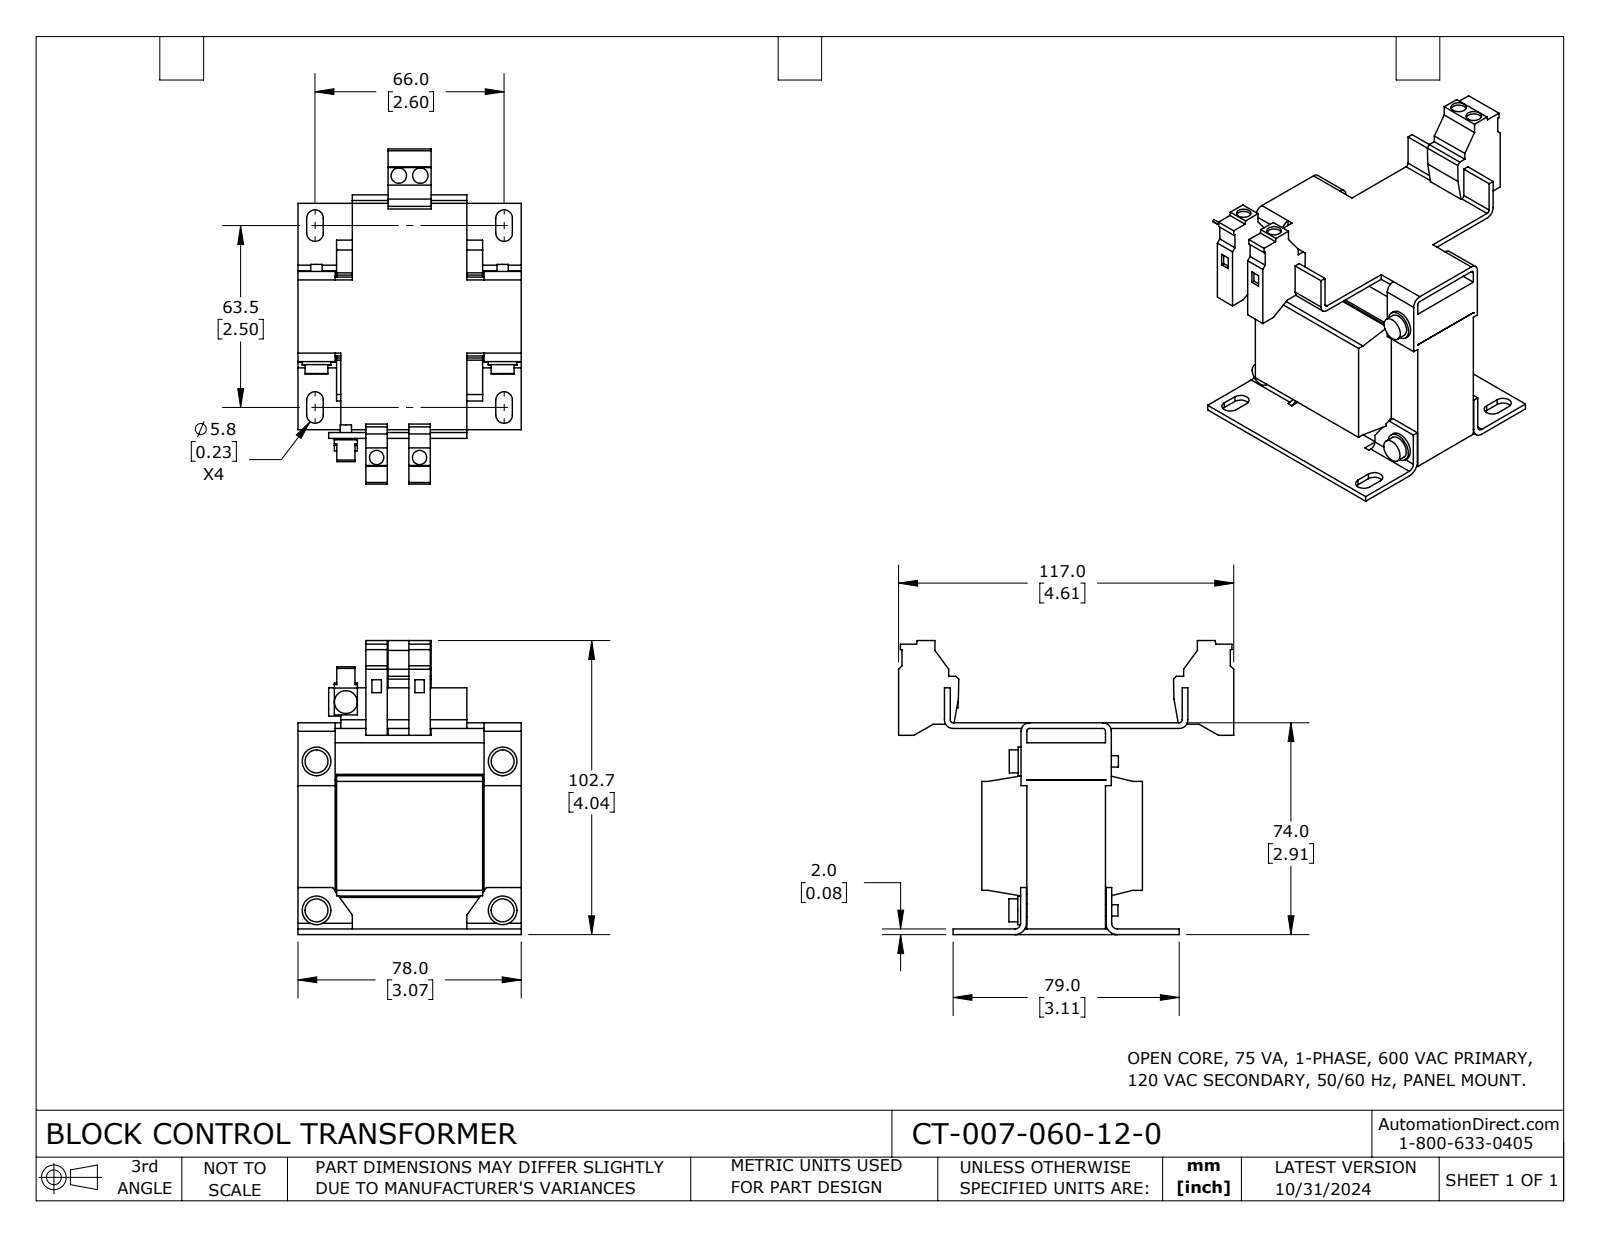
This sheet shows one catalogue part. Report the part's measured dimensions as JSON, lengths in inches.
{"part_name": "CT-007-060-12-0", "step_written_by": "SolidWorks 2023 (CONFIG_CONTROL_DESIGN)", "units": "inches", "bodies": {"solids": 1, "faces": 338, "planar": 257, "cylindrical": 81, "other": 0}, "overall_size": [4.606, 4.043, 3.071], "volume_in3": 14.47, "surface_area_in2": 96.99, "round_holes": [[0.197, 2], [0.213, 2]], "round_bosses_or_shafts": [[0.315, 5], [0.157, 5], [0.394, 4], [0.177, 2]], "partial_cylinders_radius": [[0.114, 8], [0.039, 4], [0.118, 4], [0.079, 2], [0.157, 2]], "face_to_face_distances": [0.079, 2.835, 0.531, 2.047, 0.512, 0.709, 2.559, 2.028, 2.756, 2.913], "hole_center_spacings": [0.295, 0.591, 3.874, 3.885, 3.886, 3.92]}
